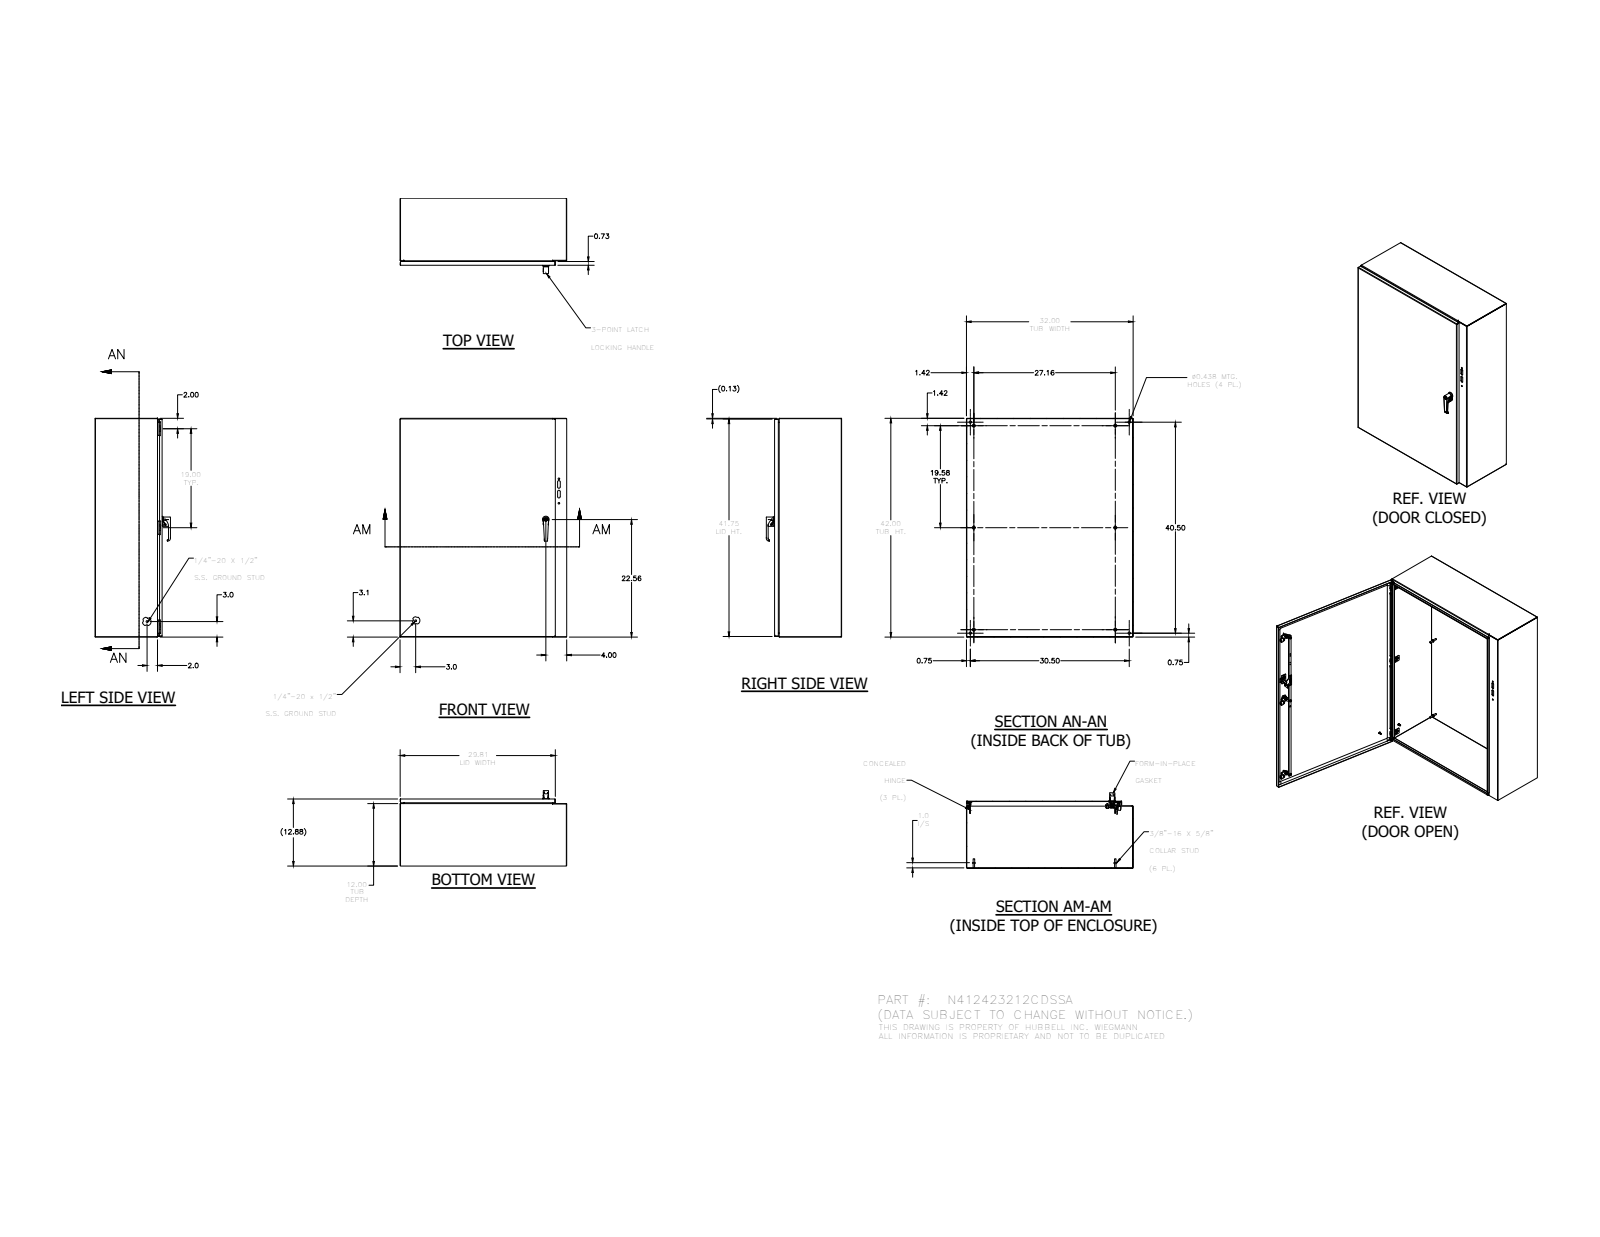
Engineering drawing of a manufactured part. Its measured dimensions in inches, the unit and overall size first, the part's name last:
Units: inches
Overall size (bounding box): 42 × 32 × 14.472
Round holes (diameter × count): ⌀0.093 ×6, ⌀0.145 ×6, ⌀0.152 ×6, ⌀0.167 ×6, ⌀0.172 ×6, ⌀0.187 ×6, ⌀0.156 ×5, ⌀0.32 ×4, ⌀0.437 ×4, ⌀0.196 ×3, ⌀0.211 ×3, ⌀0.22 ×3
Round bosses / shafts (diameter × count): ⌀0.25 ×14, ⌀0.3 ×12, ⌀0.563 ×6, ⌀0.437 ×6, ⌀0.36 ×6, ⌀0.32 ×6, ⌀0.256 ×6, ⌀0.164 ×6
Partial cylindrical surfaces — rounded edges, fillets, slot ends (radius × count): R0.02 ×38, R0.05 ×38, R0.125 ×37, R0.012 ×31, R0.031 ×28, R0.016 ×26, R0.025 ×24, R0.105 ×14
Main face-to-face distances: 0.074, 12.803, 12.729, 12.877, 31.926, 41.926, 31.852, 32, 41.852, 42
Hole centre spacings: 19, 19.25, 0.5, 16.437, 38, 19.007, 35.687, 0.66
Volume: 383.3 in³ · Surface area: 9 892 in²
Bodies: 82 solids, 2642 faces (1020 planar, 956 cylindrical, 666 other)
Part name (STEP PRODUCT): N412423212CDSSA
STEP written by: SolidWorks 2019 (AUTOMOTIVE_DESIGN)
